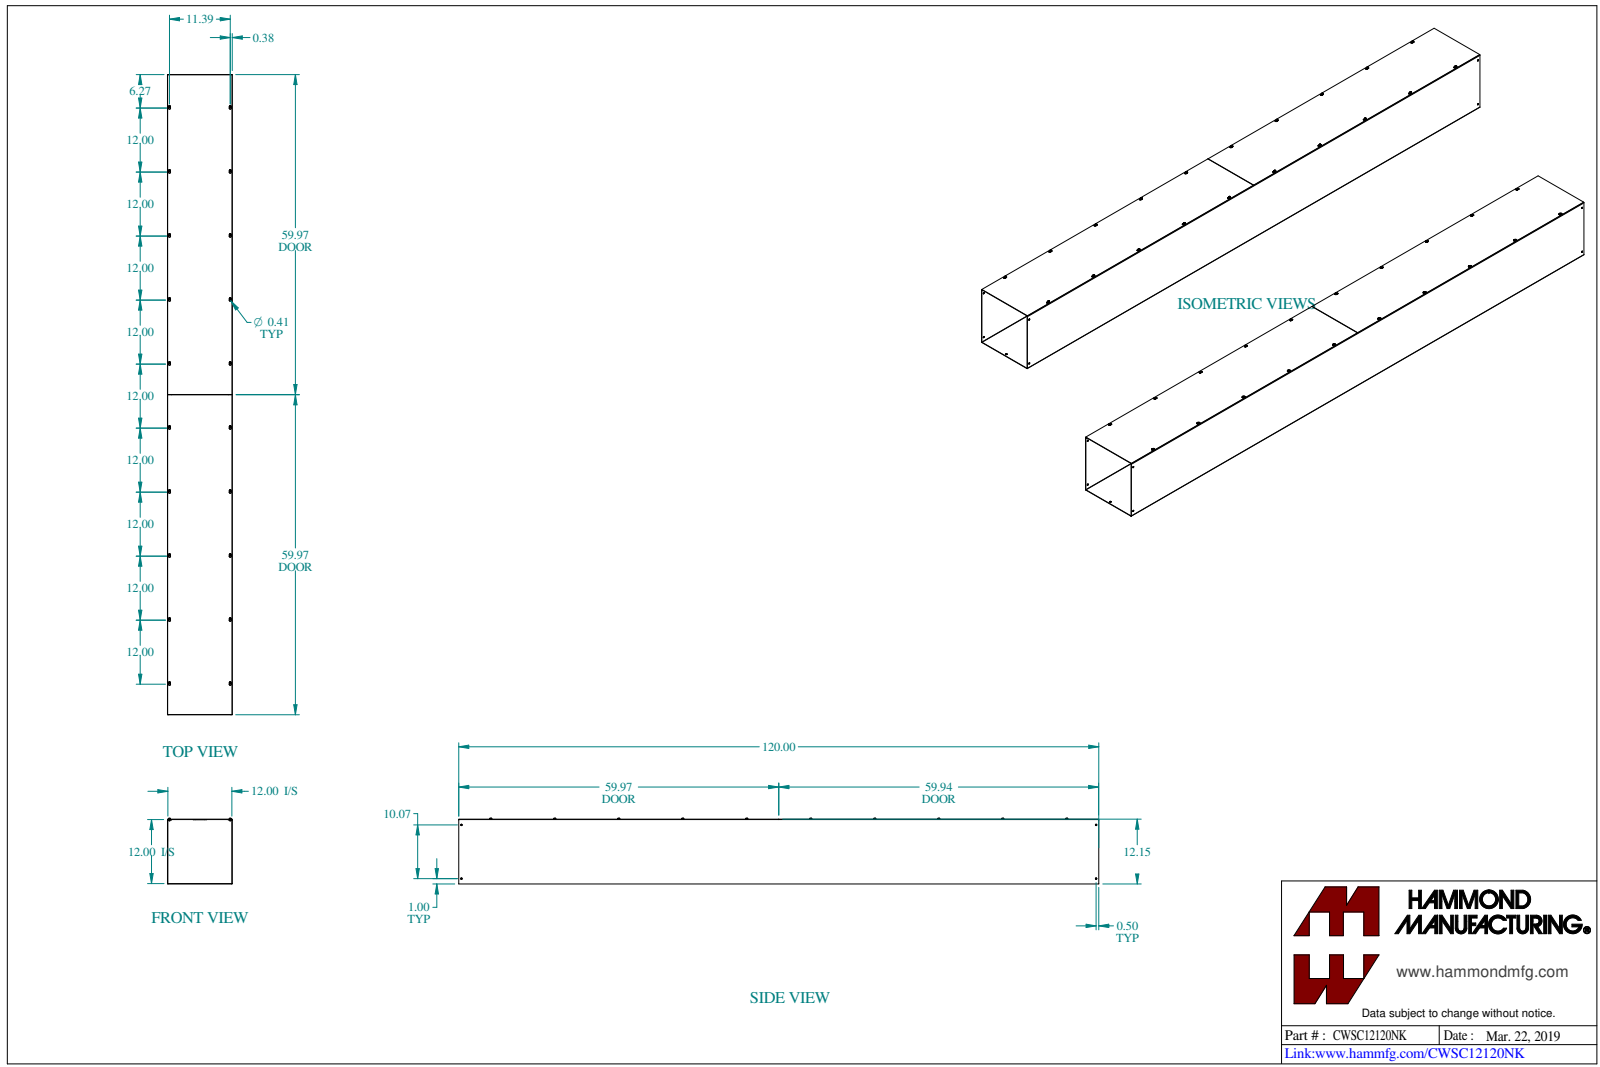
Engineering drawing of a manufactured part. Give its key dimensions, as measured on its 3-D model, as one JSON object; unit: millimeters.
{"part_name": "CWSC12120NK", "step_written_by": "SolidWorks 2023 (CONFIG_CONTROL_DESIGN)", "units": "millimeters", "bodies": {"solids": 23, "faces": 682, "planar": 334, "cylindrical": 228, "other": 120}, "overall_size": [3048, 313.1, 308.5], "volume_mm3": 7143000, "surface_area_mm2": 7686000, "round_holes": [[4.5, 20], [6.8, 4], [8, 2]], "round_bosses_or_shafts": [[9.5, 20], [4.8, 20]], "partial_cylinders_radius": [[3.2, 20], [5.2, 20], [0.9, 4], [2.7, 4]], "face_to_face_distances": [1.8, 306.6, 304.8, 2, 308.6, 306.8, 308.5, 303, 3.8, 0.8], "hole_center_spacings": [304.8, 420.3, 609.6, 674.8, 914.4, 959.1, 1219.2, 1253.1]}
